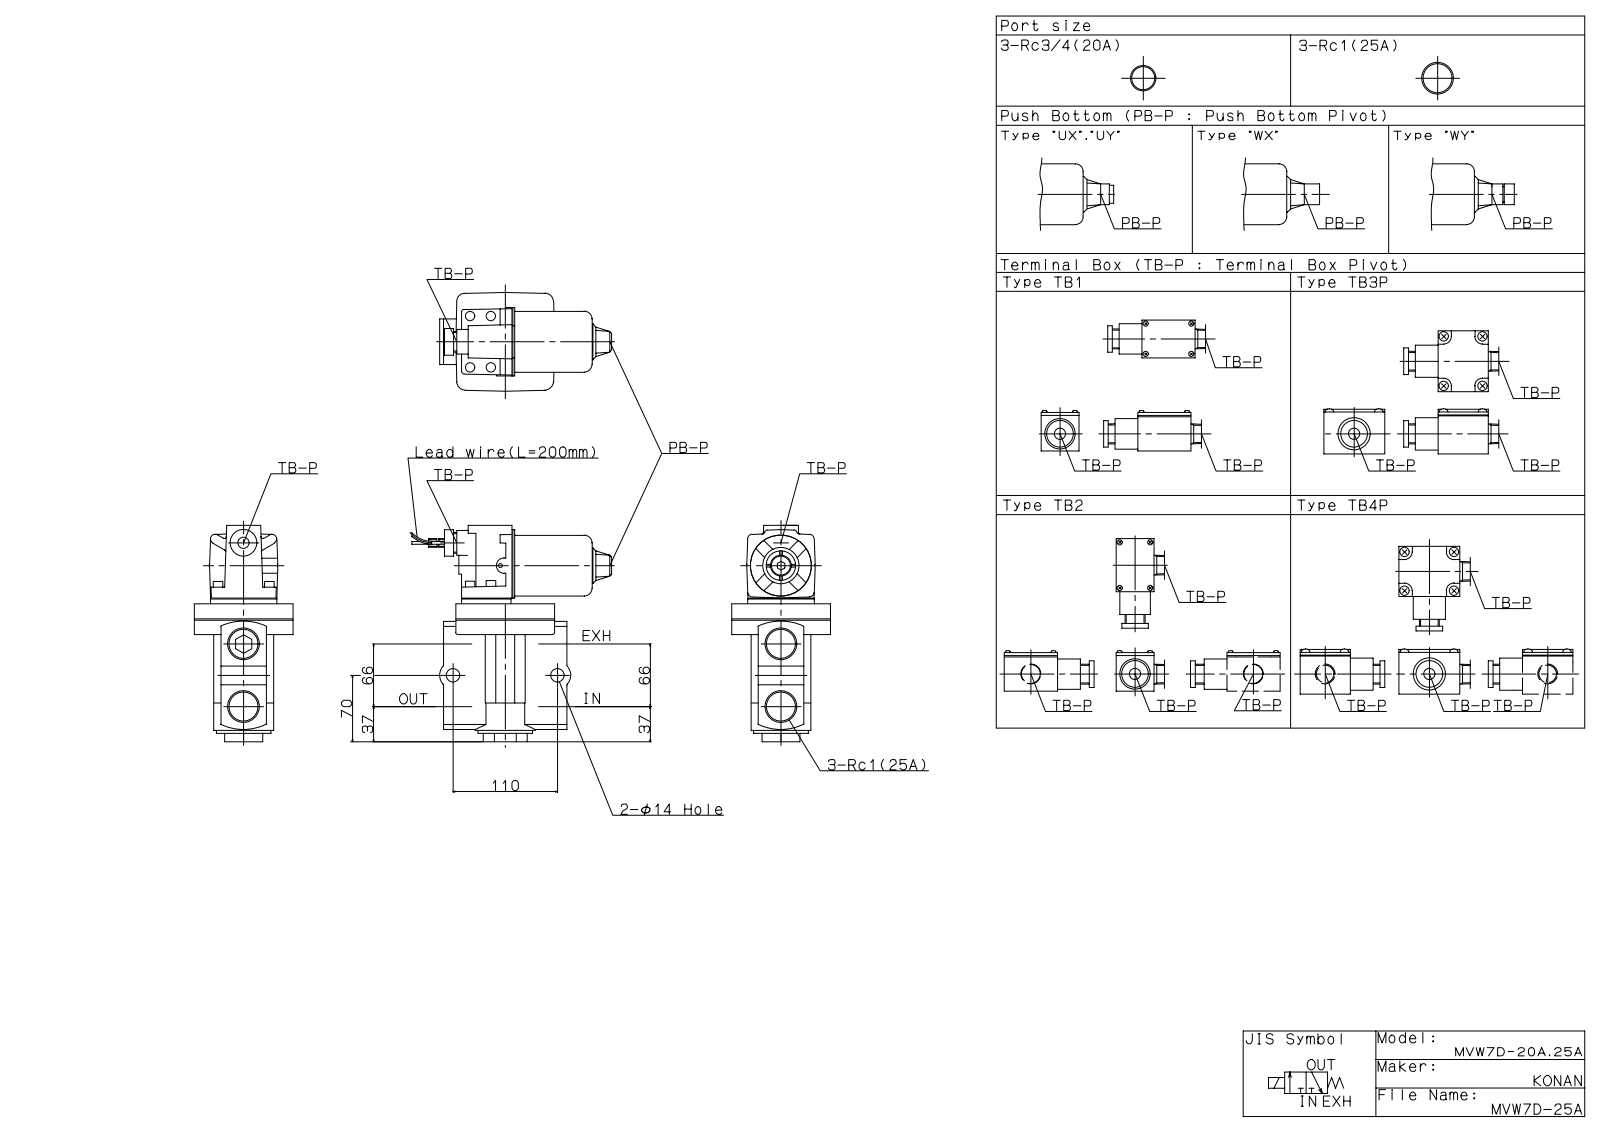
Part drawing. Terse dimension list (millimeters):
name: MVW7D-25A
written by: SolidWorks 2023 (AUTOMOTIVE_DESIGN)
unit: mm
bodies: 1 solid, 127 faces (77 planar, 50 cylindrical, 0 other)
size: 230 × 181 × 104
volume: 1 525 000 mm³; area: 123 349 mm²
holes: 2× ⌀34
bosses: 4× ⌀5.6, 1× ⌀64, 1× ⌀57.5, 1× ⌀41, 1× ⌀28, 1× ⌀26, 1× ⌀24, 1× ⌀22
rounds: 4× R4, 4× R9, 2× R5, 2× R14, 1× R10, 1× R11.5
face distances: 48, 104, 13, 55.5, 28, 76, 32, 18, 6, 117
hole spacings: 66
